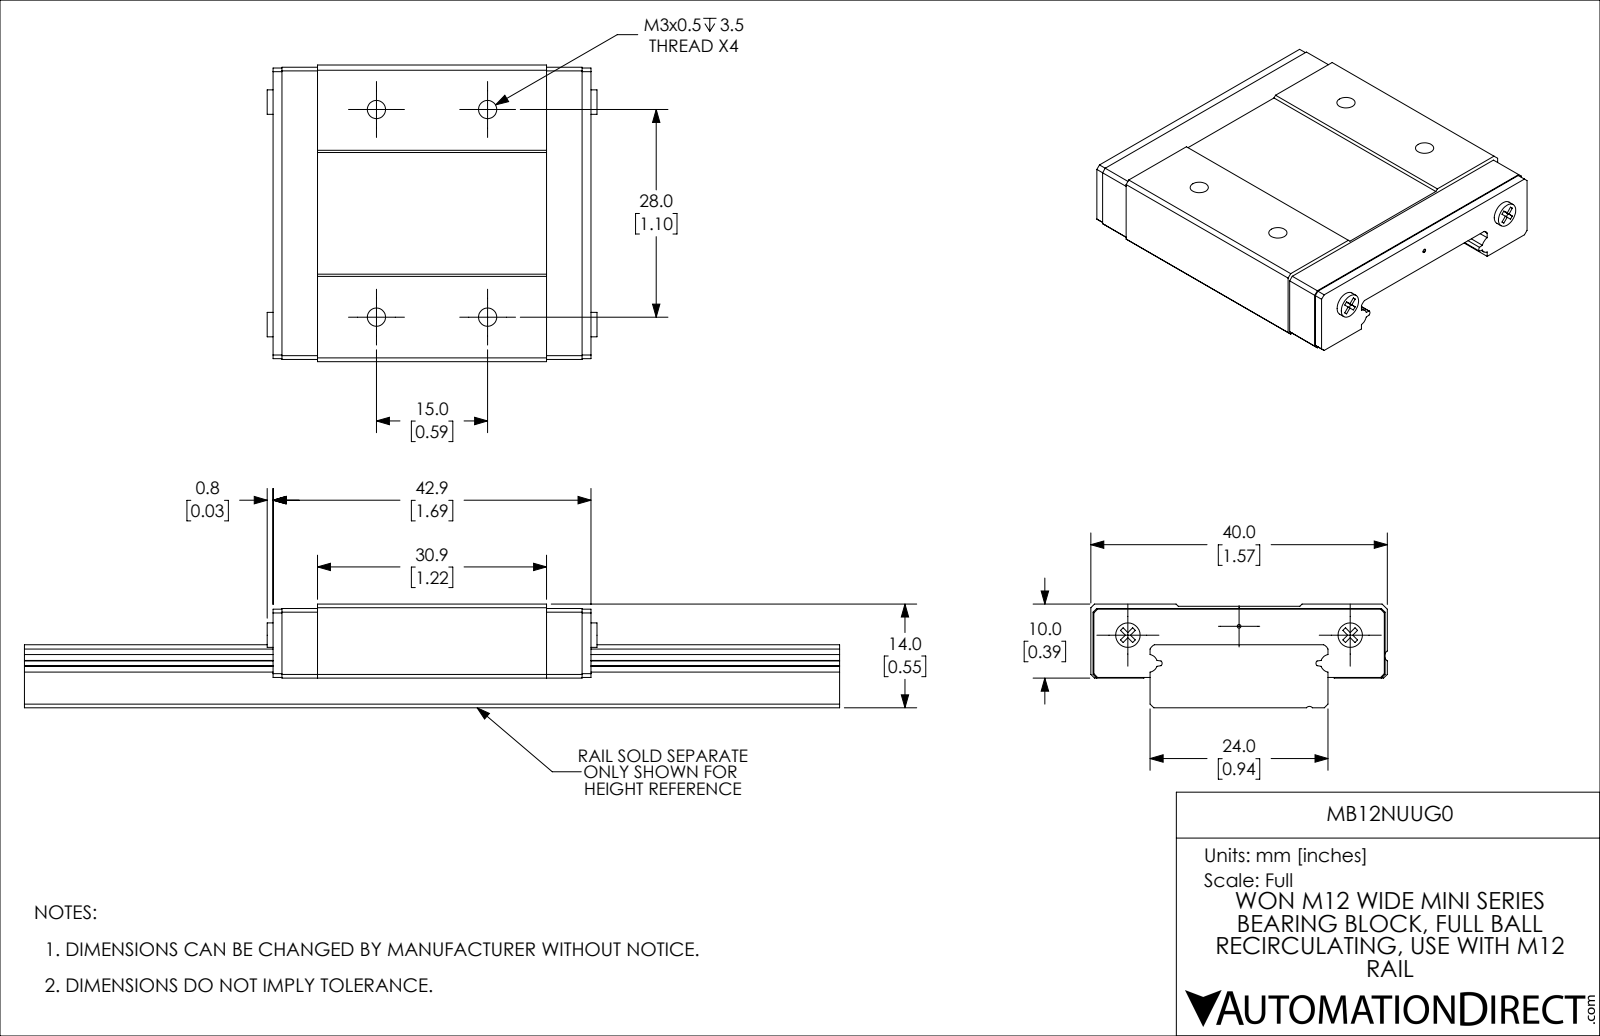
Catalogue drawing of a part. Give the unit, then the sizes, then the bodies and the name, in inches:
Units: inches
Overall size (bounding box): 1.752 × 1.575 × 0.394
Round holes (diameter × count): ⌀0.097 ×4, ⌀0.02 ×1
Round bosses / shafts (diameter × count): ⌀0.13 ×2
Partial cylindrical surfaces — rounded edges, fillets, slot ends (radius × count): R0.017 ×2, R0.045 ×2, R0.047 ×2, R0.031 ×1
Main face-to-face distances: 0.217, 0.177, 0.394, 0.382, 0.205, 0.37, 0.193, 0.024, 1.689, 1.575
Hole centre spacings: 0.591, 1.102, 1.25
Volume: 0.739 in³ · Surface area: 8.528 in²
Bodies: 1 solid, 158 faces (120 planar, 30 cylindrical, 8 other)
Part name (STEP PRODUCT): MB12NUUG0
STEP written by: SolidWorks 2019 (CONFIG_CONTROL_DESIGN)
